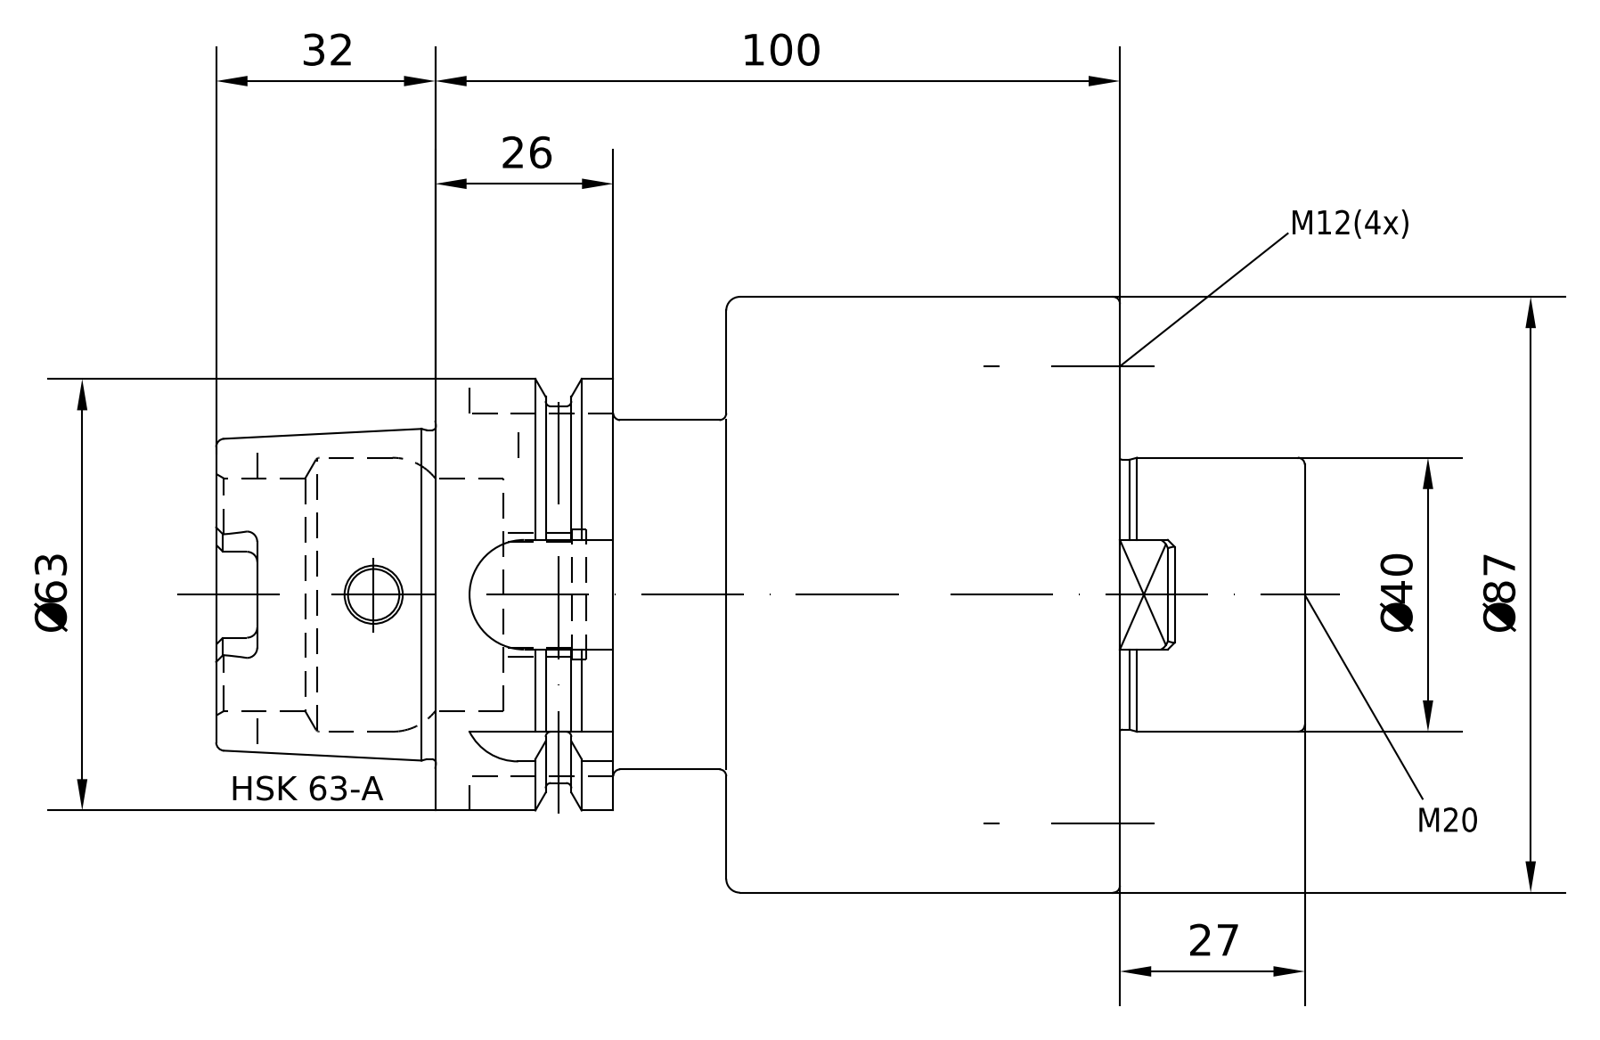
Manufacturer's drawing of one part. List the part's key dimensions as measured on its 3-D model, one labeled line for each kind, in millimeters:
Part name (STEP PRODUCT): A63-051-40
STEP written by: PRO/ENGINEER BY PARAMETRIC TECHNOLOGY CORPORATION, 2010430 (CONFIG_CONTROL_DESIGN)
Units: millimetres
Bodies: 1 solid, 226 faces (74 planar, 70 cylindrical, 82 other)
Overall size (bounding box): 159 × 87 × 87
Volume: 475 265 mm³ · Surface area: 63 732 mm²
Round holes (diameter × count): ⌀10.2 ×4, ⌀12 ×4, ⌀7.5 ×1, ⌀10 ×1, ⌀16.92 ×1, ⌀17.5 ×1, ⌀18.32 ×1, ⌀18.66 ×1, ⌀20 ×1, ⌀34 ×1, ⌀40 ×1
Round bosses / shafts (diameter × count): ⌀87 ×1, ⌀63 ×1, ⌀55 ×1, ⌀51 ×1, ⌀48.04 ×1, ⌀18 ×1
Partial cylindrical surfaces — rounded edges, fillets, slot ends (radius × count): R1.5 ×6, R3 ×4, R8 ×1, R8.02 ×1, R9.02 ×1
Main face-to-face distances: 57.5, 42.5, 100, 16, 127, 84.5, 27, 26, 16.5, 74
Hole centre spacings: 33.35, 47.16, 66.69
